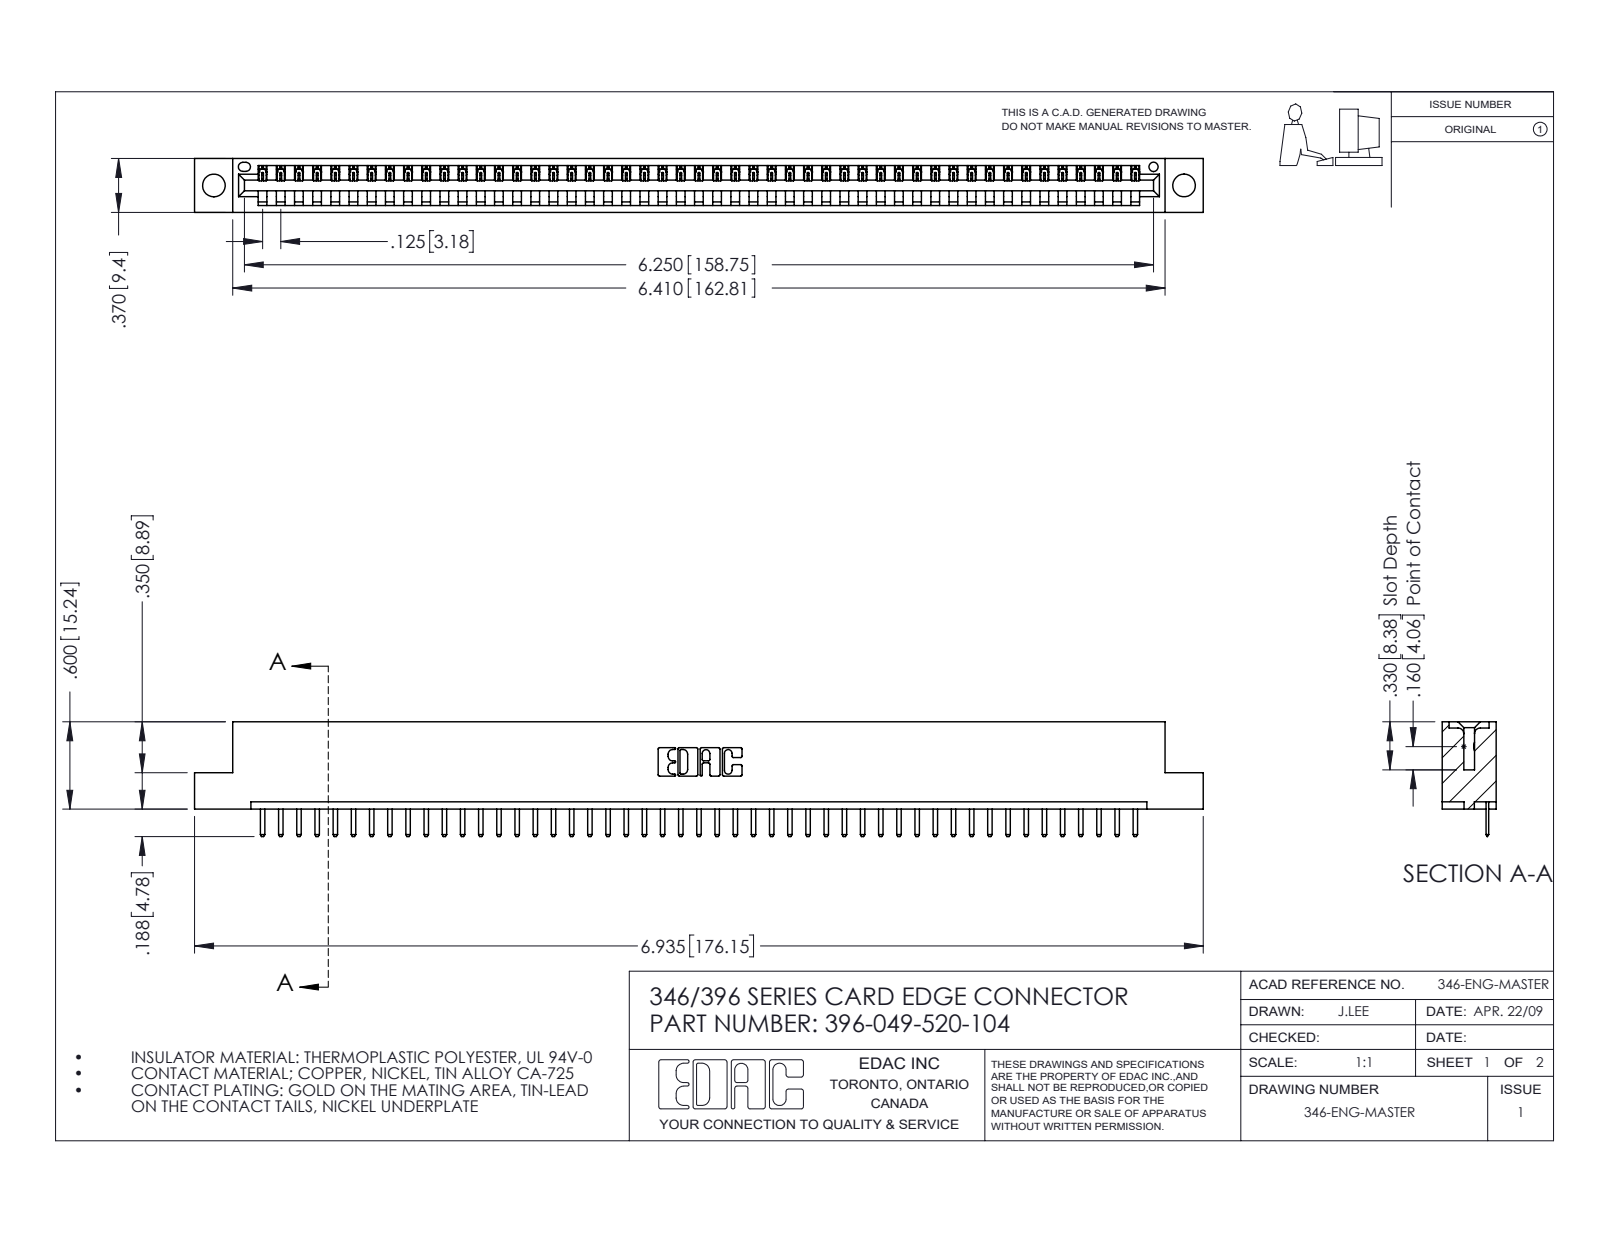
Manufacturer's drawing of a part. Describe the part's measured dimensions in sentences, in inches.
The part is named "396-049-520-104; 345-292-001_345-293-120; 346 Part_Flush Mounting Lugs - 0.156 Dia-TH". Its 3-D file was written by "SolidWorks 2016 (CONFIG_CONTROL_DESIGN)". It is 50 solids with 3160 faces: 2134 planar, 1026 cylindrical and 0 other. Overall it measures 6.935 by 0.788 by 0.37 inches. Its volume is 1.018 cubic inches and its surface area 31.4 square inches. Round holes: 2 of diameter 0.156, 1 of diameter 0.064. Partial cylindrical surfaces (rounded edges, fillets, slot ends): 100 of radius 0.01, 98 of radius 0.006, 22 of radius 0.01, 6 of radius 0.007, 6 of radius 0.031, 3 of radius 0.026, 2 of radius 0.031, 2 of radius 0.04. The main face-to-face distances are 0.048, 0.322, 0.37, 0.25, 0.148, 0.222, 0.1, 0.174, 0.072, 0.298. The hole center spacings are 0.246, 6.461, 6.67.
